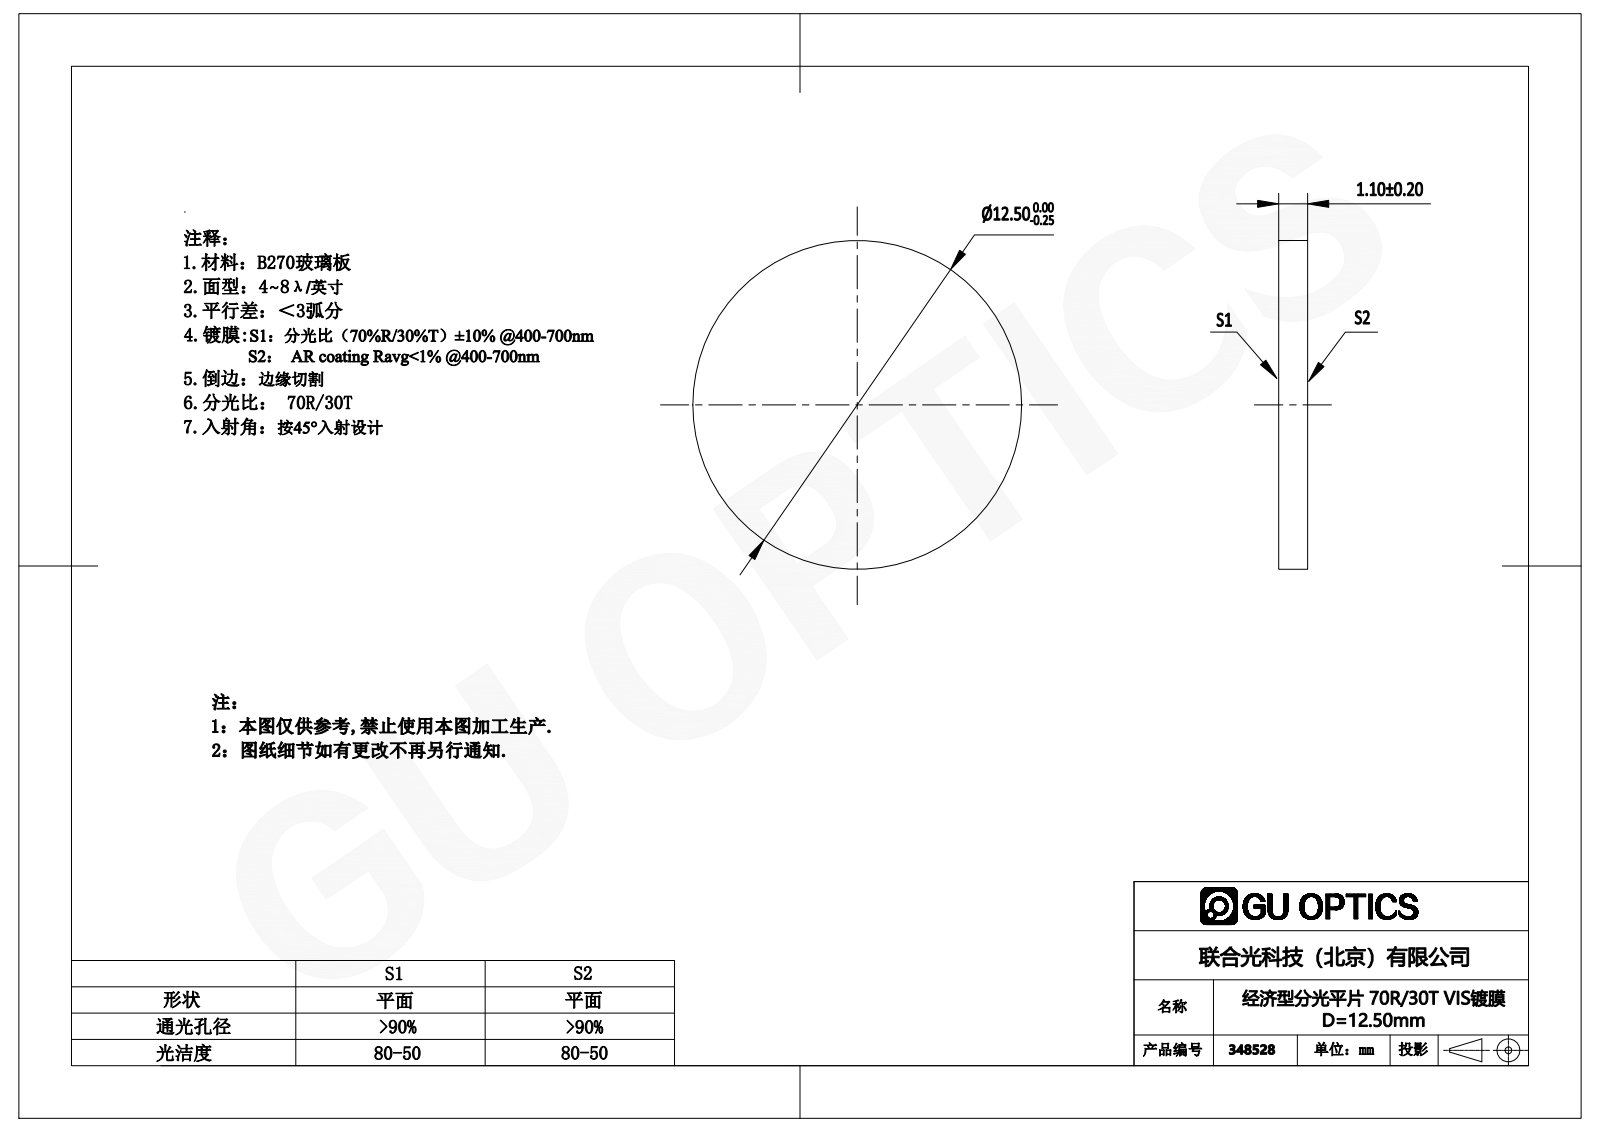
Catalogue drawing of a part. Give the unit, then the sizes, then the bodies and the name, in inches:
Units: inches
Overall size (bounding box): 0.492 × 0.492 × 0.043
Round bosses / shafts (diameter × count): ⌀0.492 ×1
Main face-to-face distances: 0.043
Volume: 0.008 in³ · Surface area: 0.448 in²
Bodies: 1 solid, 4 faces (2 planar, 2 cylindrical, 0 other)
Part name (STEP PRODUCT): 348500
STEP written by: SolidWorks 2016 (CONFIG_CONTROL_DESIGN)
